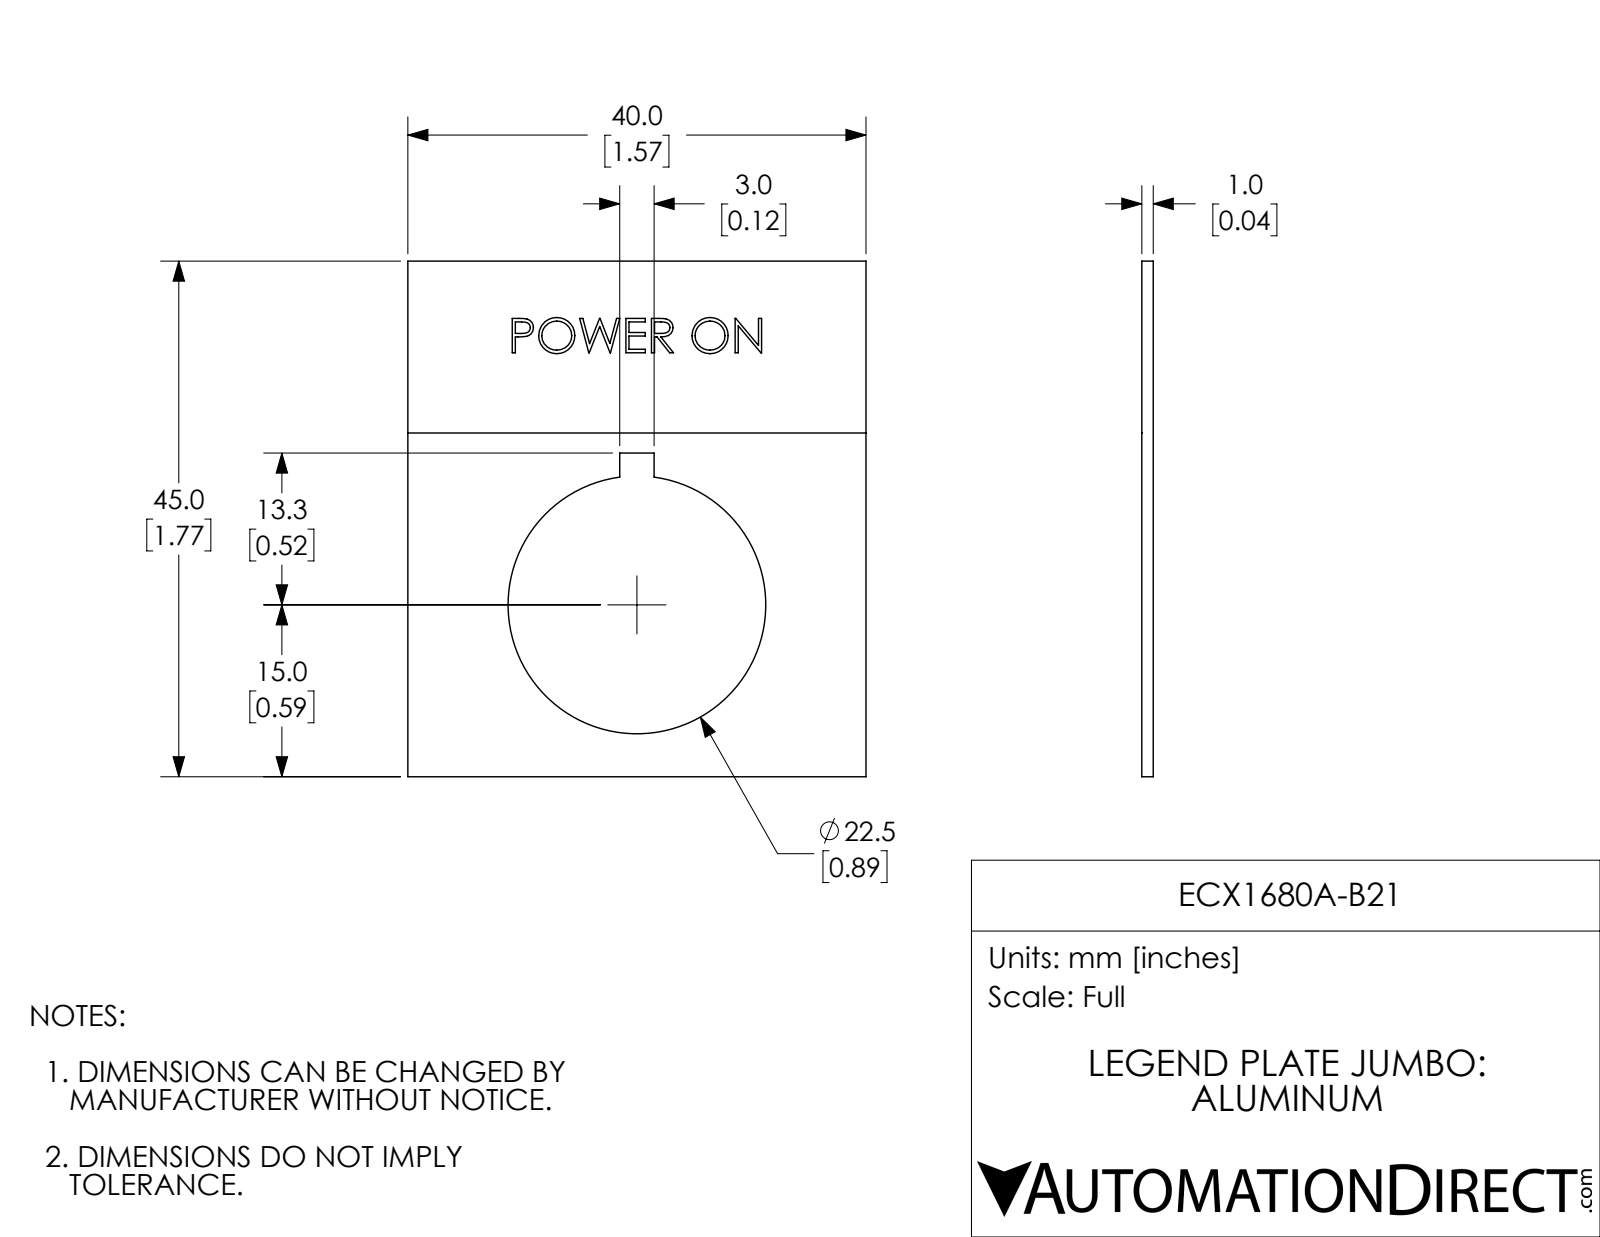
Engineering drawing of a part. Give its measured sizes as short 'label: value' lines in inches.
name: ECX1680A-B21
written by: SolidWorks 2017 (AUTOMOTIVE_DESIGN)
unit: in
bodies: 1 solid, 106 faces (76 planar, 3 cylindrical, 27 other)
size: 1.772 × 1.575 × 0.039
volume: 0.085 in³; area: 4.709 in²
holes: 1× ⌀0.886
face distances: 0.039, 0.039, 1.575, 1.772, 0.846, 0.728, 1.112, 0.659, 0.118, 1.181
